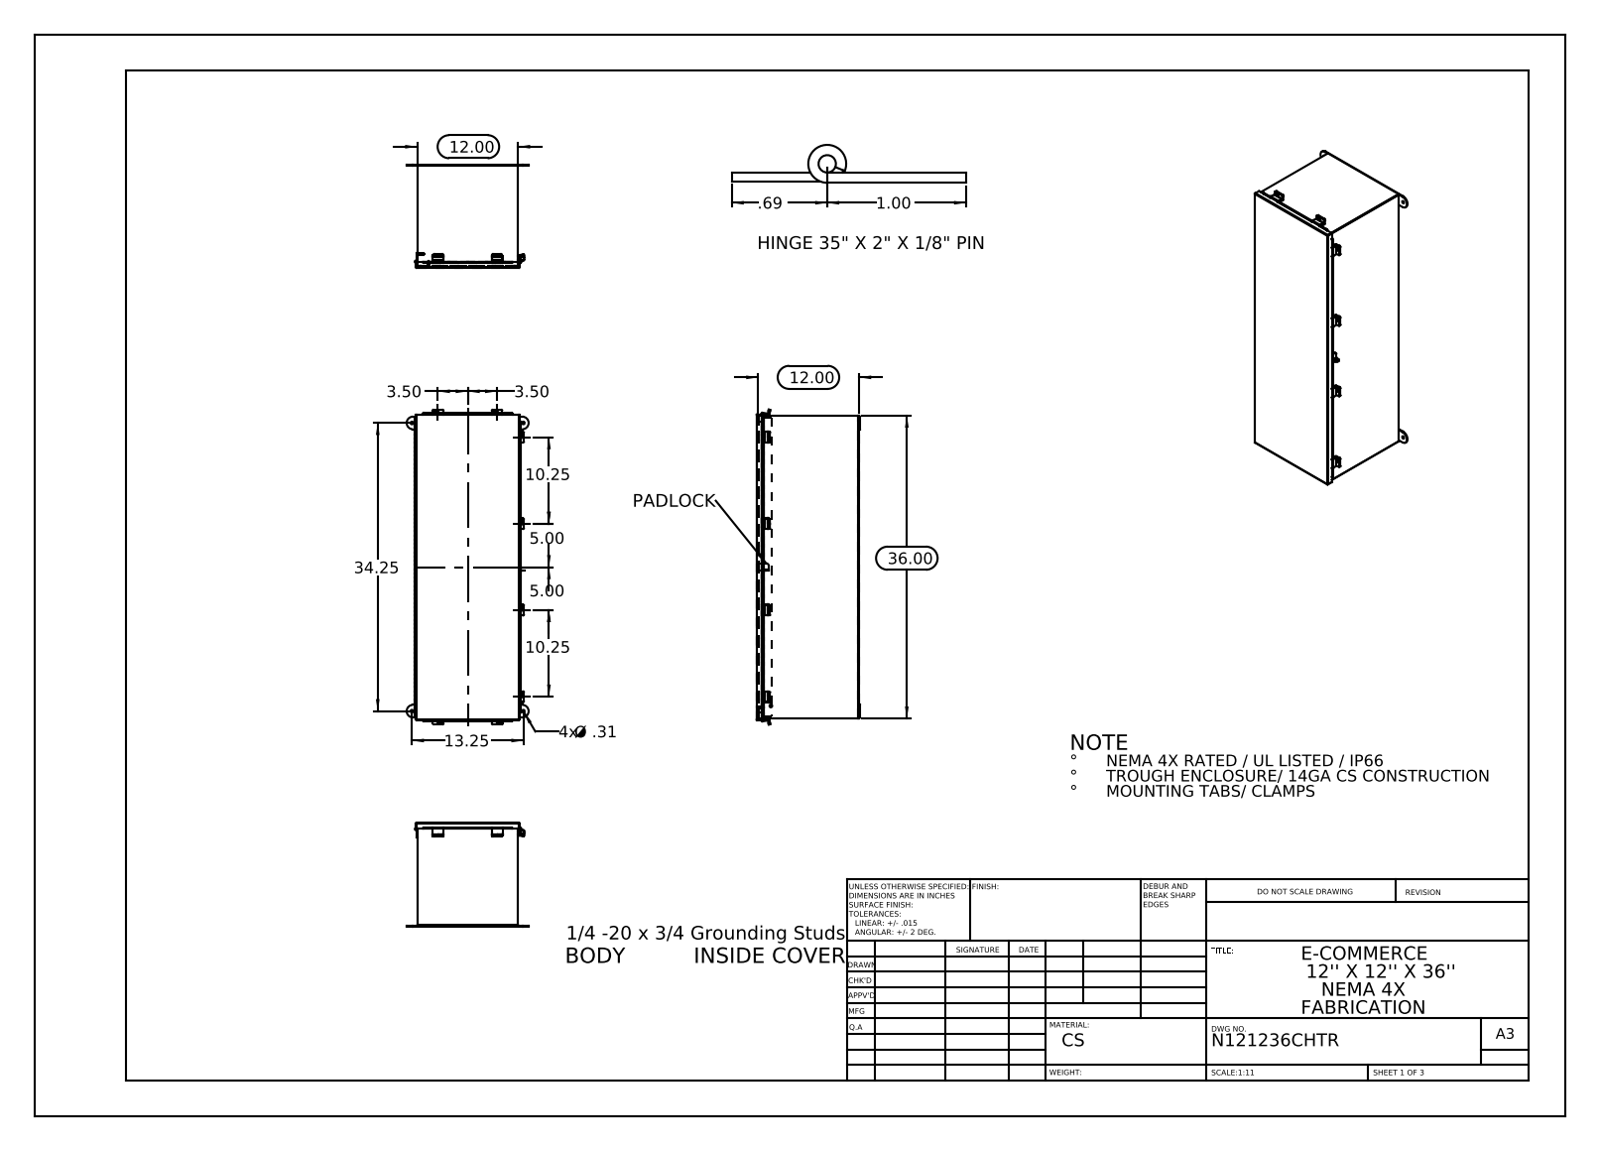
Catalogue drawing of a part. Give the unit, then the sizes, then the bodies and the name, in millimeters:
Units: millimetres
Overall size (bounding box): 950.1 × 368.3 × 313.4
Round holes (diameter × count): ⌀6.4 ×8, ⌀8 ×4, ⌀3.2 ×1, ⌀9.5 ×1
Round bosses / shafts (diameter × count): ⌀8 ×2, ⌀6 ×2, ⌀6.9 ×1, ⌀6.4 ×1
Partial cylindrical surfaces — rounded edges, fillets, slot ends (radius × count): R3.2 ×28, R3.4 ×16, R0.2 ×12, R0.3 ×10, R2.2 ×10, R2.1 ×6, R2.5 ×6, R19.1 ×4
Main face-to-face distances: 1.9, 302.9, 308.1, 304.8, 301, 310, 306.1, 912.5, 910.6, 914.4
Hole centre spacings: 177.8, 261.3, 336.6, 522.3, 870, 932.8, 261, 320.9
Volume: 2 789 000 mm³ · Surface area: 2 936 000 mm²
Bodies: 27 solids, 1252 faces (769 planar, 463 cylindrical, 20 other)
Part name (STEP PRODUCT): N121236SSCHTR JIC Enclosure Template; N121236SSCHTR Hinge Cover Side JIC; N121236SSCHTR _JIC Hinge; N121236SSCHTR JIC Mounting Bracket (+8 more)
STEP written by: SolidWorks 2013 (CONFIG_CONTROL_DESIGN)
